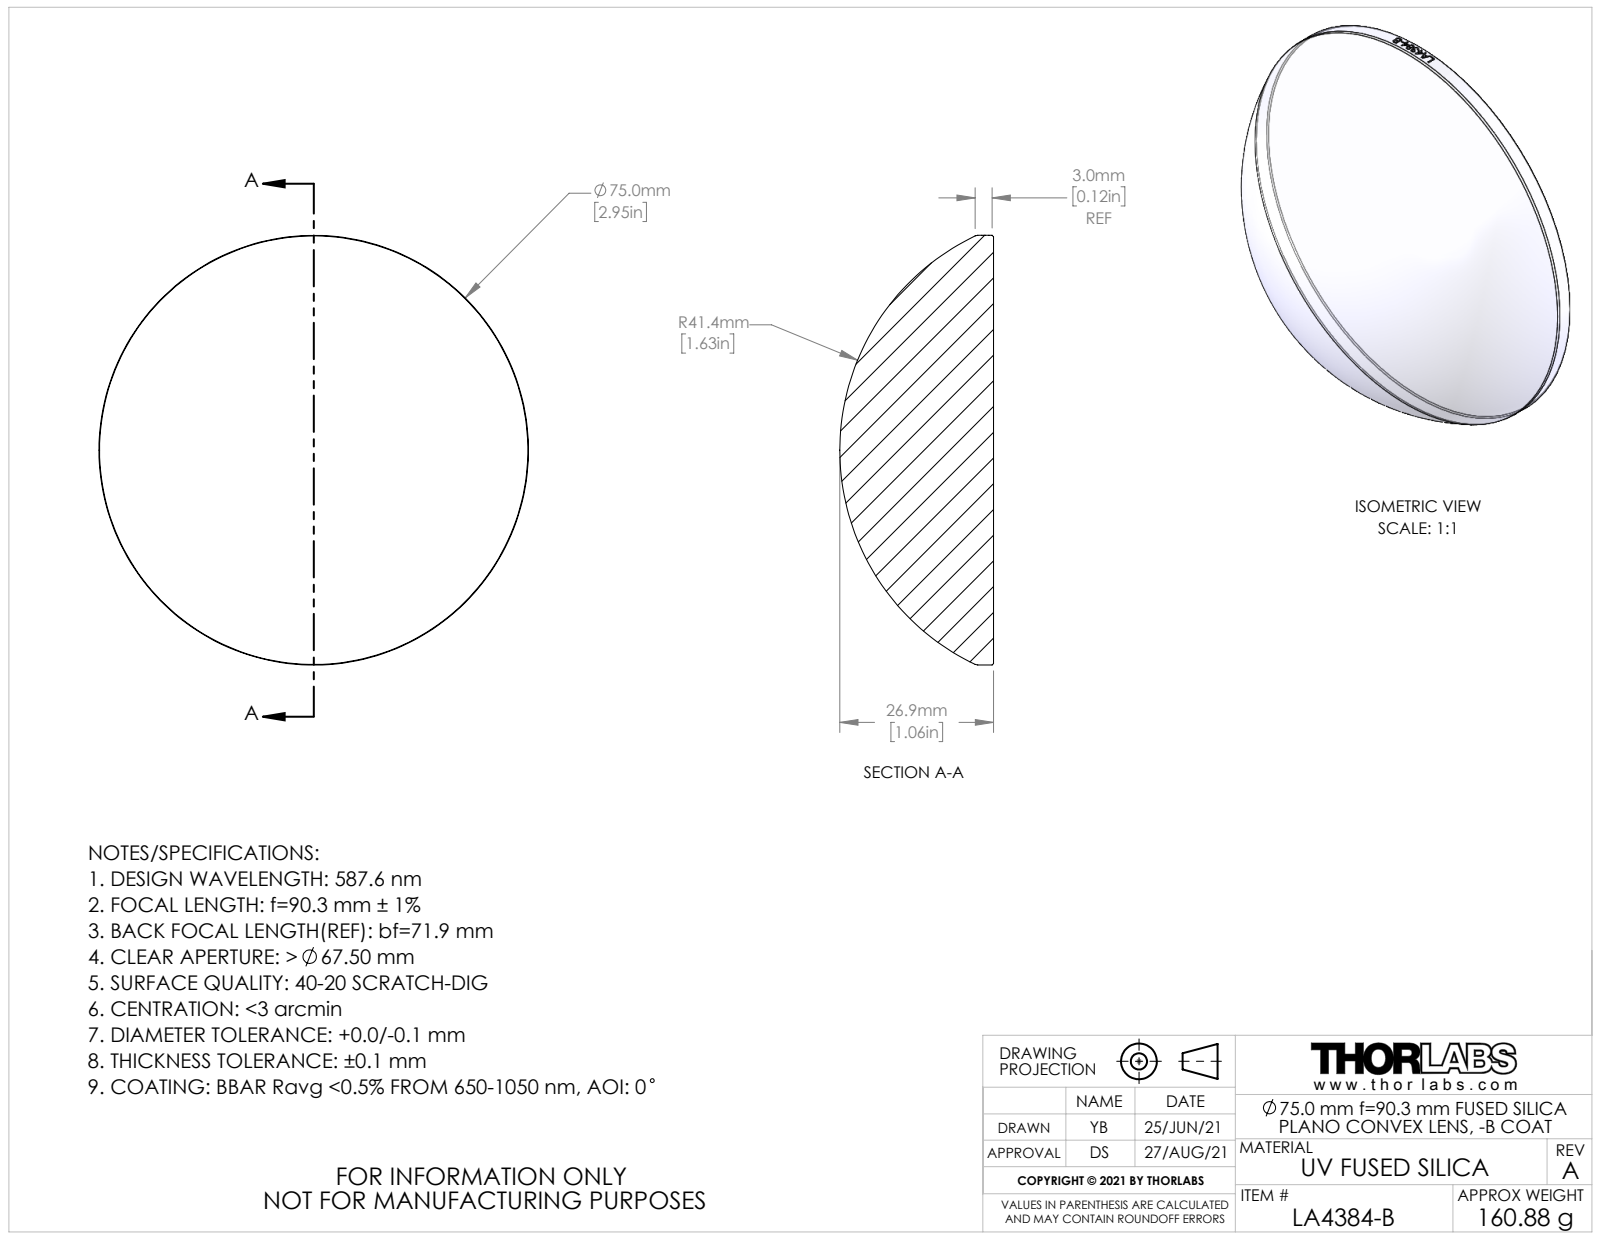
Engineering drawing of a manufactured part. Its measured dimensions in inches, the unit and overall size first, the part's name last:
Units: inches
Overall size (bounding box): 2.953 × 2.953 × 1.057
Round bosses / shafts (diameter × count): ⌀2.953 ×1
Volume: 4.456 in³ · Surface area: 17.5 in²
Bodies: 1 solid, 24 faces (1 planar, 17 cylindrical, 6 other)
Part name (STEP PRODUCT): CTN017913-E0W
STEP written by: SolidWorks 2018 (AUTOMOTIVE_DESIGN)
